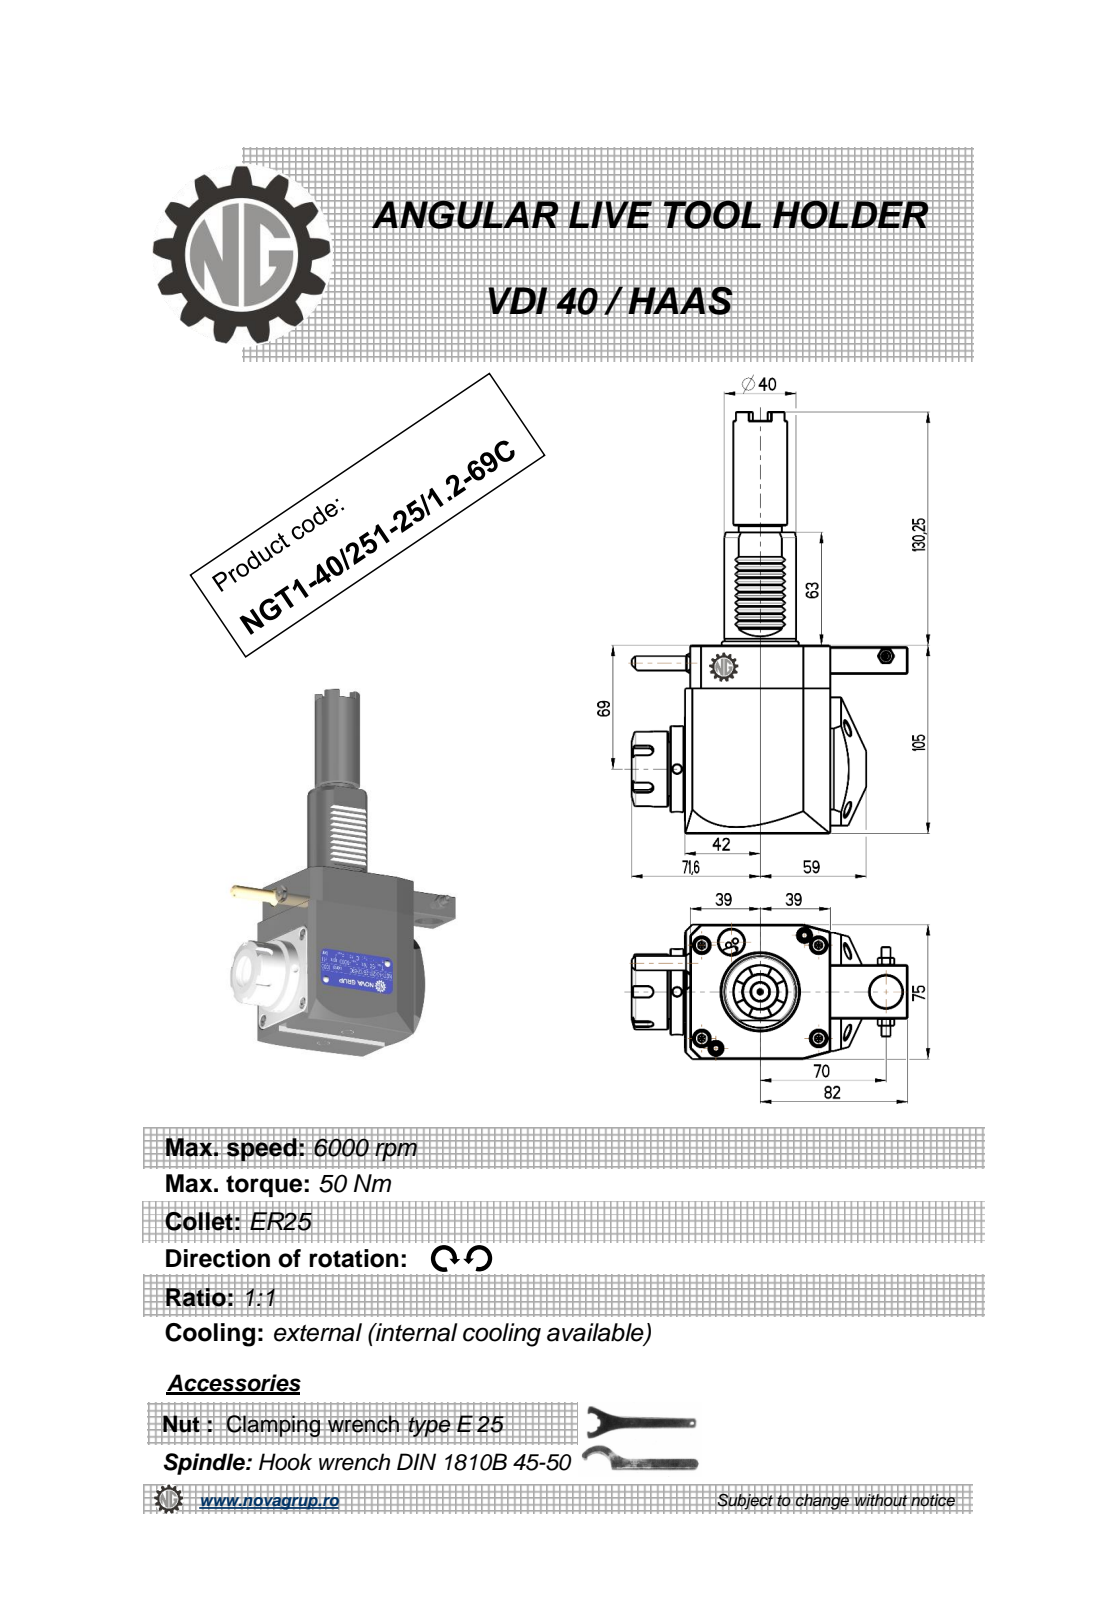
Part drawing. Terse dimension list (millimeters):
name: NGT1_40_251_25_1_2_69C
written by: PRO/ENGINEER BY PARAMETRIC TECHNOLOGY CORPORATION, 2010280 (CONFIG_CONTROL_DESIGN)
unit: mm
bodies: 1 solid, 482 faces (227 planar, 92 cylindrical, 163 other)
size: 235.25 × 153.6 × 76.6
volume: 844 481 mm³; area: 75 255 mm²
holes: 3× ⌀5, 1× ⌀3, 1× ⌀4.2, 1× ⌀9.5, 1× ⌀18, 1× ⌀19.5, 1× ⌀20.3
bosses: 1× ⌀48, 1× ⌀42, 1× ⌀40, 1× ⌀37.5, 1× ⌀33, 1× ⌀30, 1× ⌀24, 1× ⌀10
rounds: 12× R0.26, 10× R0.3, 6× R0.2, 5× R3, 1× R0.5, 1× R40
face distances: 75, 105, 81, 89, 80.8, 1, 3, 2.8, 78, 8
hole spacings: 16.19, 46.25, 61.13, 61.5, 70, 116.25, 132.22
